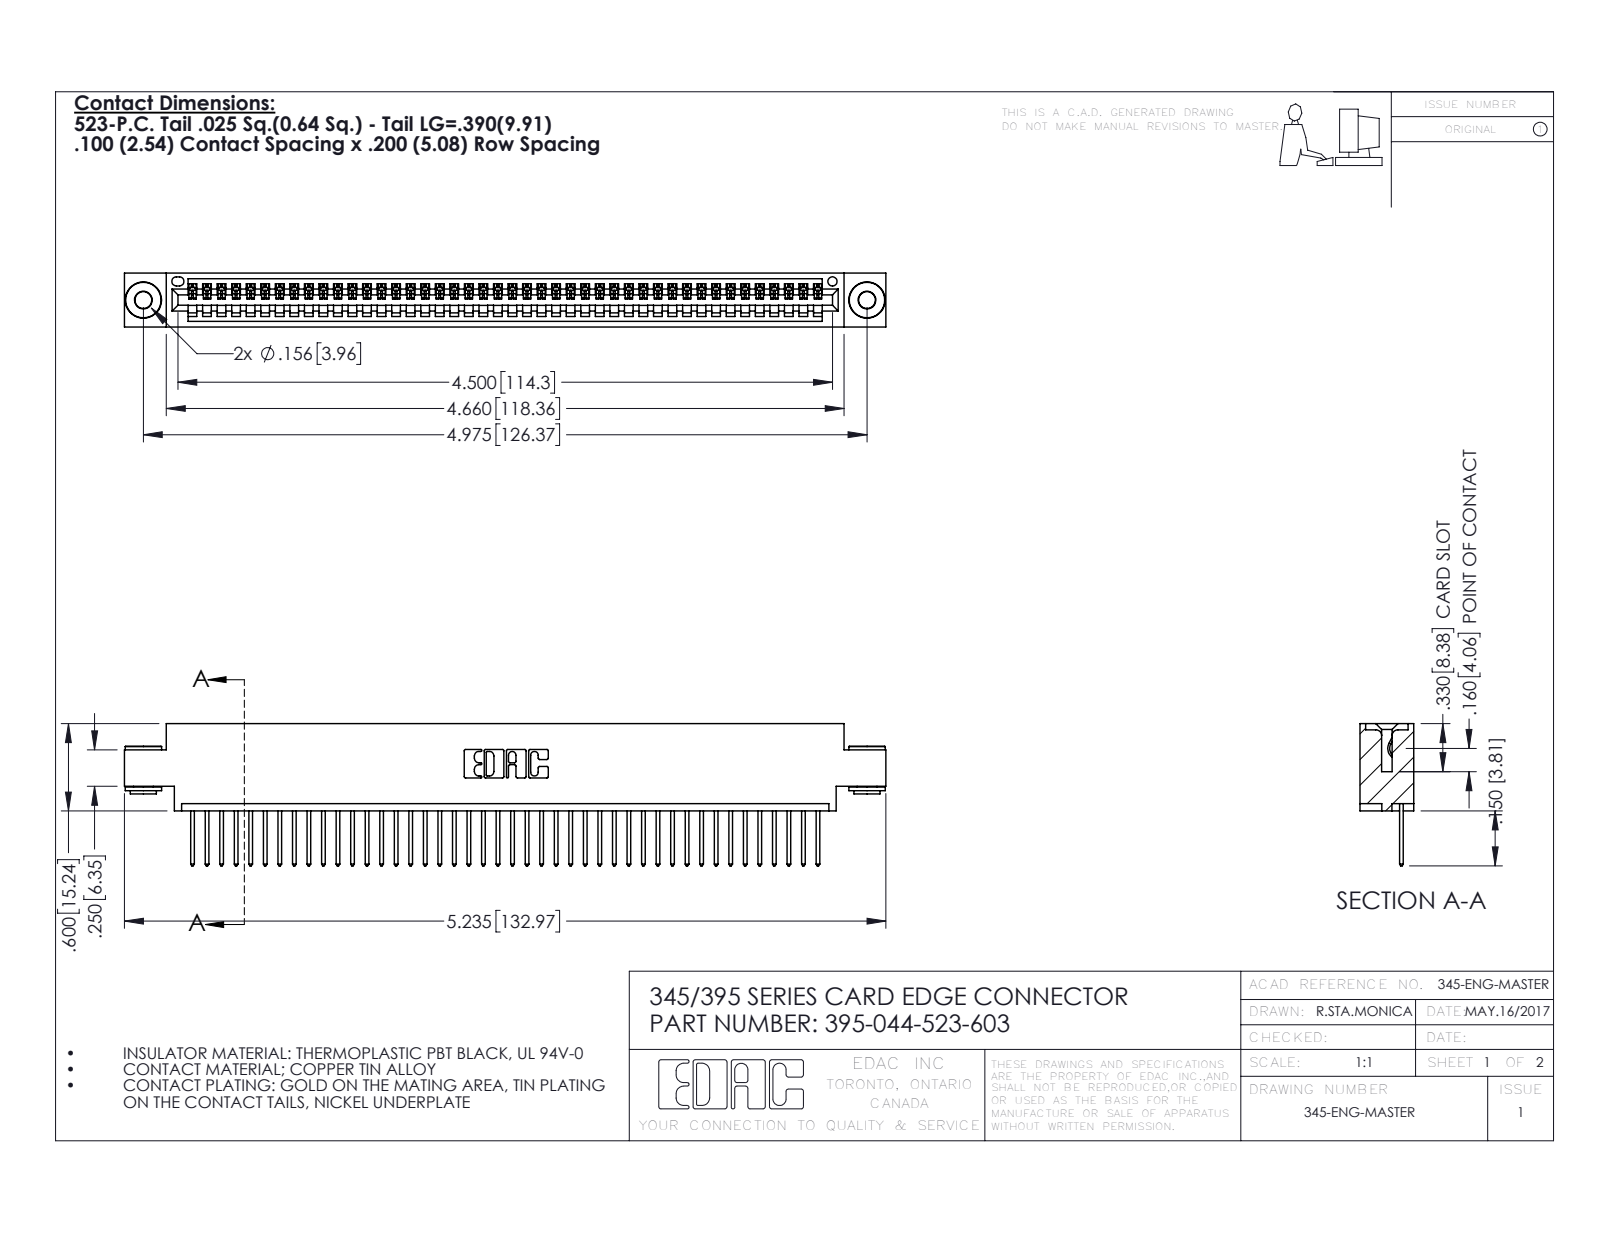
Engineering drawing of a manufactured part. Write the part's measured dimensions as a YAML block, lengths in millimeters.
part_name: "395-044-523-603; 345 Part_0.170 Offset - 0.156 Dia-TH; 345-250-002_345-250-002-102; 345-292-001_345-293-123"
step_written_by: "SolidWorks 2016 (CONFIG_CONTROL_DESIGN)"
units: millimeters
bodies: {solids: 47, faces: 2720, planar: 1854, cylindrical: 858, other: 8}
overall_size: [133, 24.8, 9.4]
volume: 12500
surface_area: 17070
round_holes:
  - {diameter: 2.9, count: 2}
  - {diameter: 4, count: 2}
  - {diameter: 1.6, count: 1}
round_bosses_or_shafts:
  - {diameter: 6.4, count: 2}
  - {diameter: 4.6, count: 2}
  - {diameter: 3.5, count: 2}
partial_cylinders:
  - {radius: 0.2, count: 88}
  - {radius: 0.3, count: 88}
  - {radius: 0.3, count: 22}
  - {radius: 0.2, count: 6}
  - {radius: 0.8, count: 6}
  - {radius: 0.7, count: 3}
  - {radius: 0.8, count: 2}
  - {radius: 1, count: 2}
face_to_face_distances: [1.8, 7.6, 9.4, 5.1, 2.5, 6.9, 0.6, 5.7, 4.4, 3.8]
hole_center_spacings: [6.9, 120.4, 126.4]
